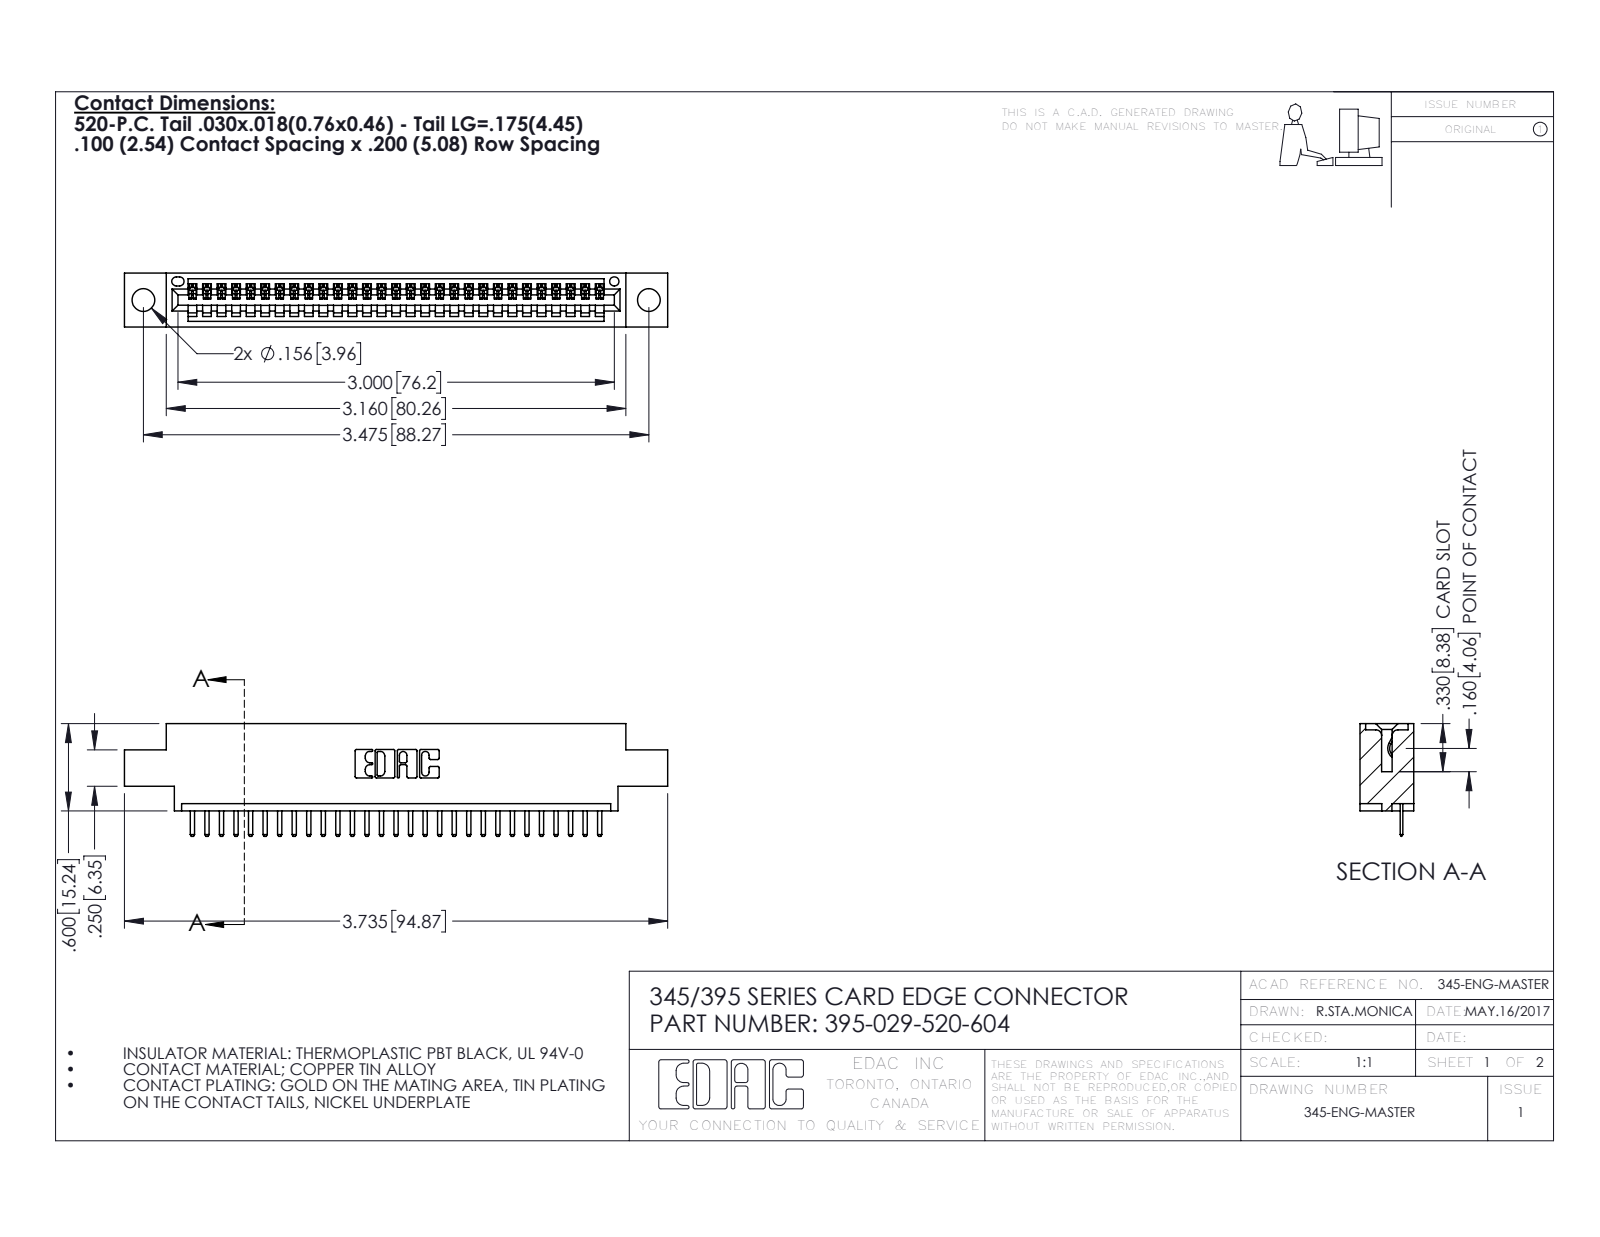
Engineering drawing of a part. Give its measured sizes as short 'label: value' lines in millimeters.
name: 345-292-001_345-293-120; 395-029-520-604; 345 Part_0.170 Offset - 0.156 Dia-TH
written by: SolidWorks 2016 (CONFIG_CONTROL_DESIGN)
unit: mm
bodies: 30 solids, 1928 faces (1302 planar, 626 cylindrical, 0 other)
size: 94.9 × 19.7 × 9.4
volume: 8 620 mm³; area: 10 940 mm²
holes: 2× ⌀4, 1× ⌀1.6
rounds: 60× R0.3, 58× R0.2, 22× R0.3, 6× R0.2, 6× R0.8, 3× R0.7, 2× R0.8, 2× R1
face distances: 7.6, 1.8, 9.4, 5.1, 2.5, 6.9, 0.6, 5.7, 1.8, 4.4
hole spacings: 6.9, 82.3, 88.3
